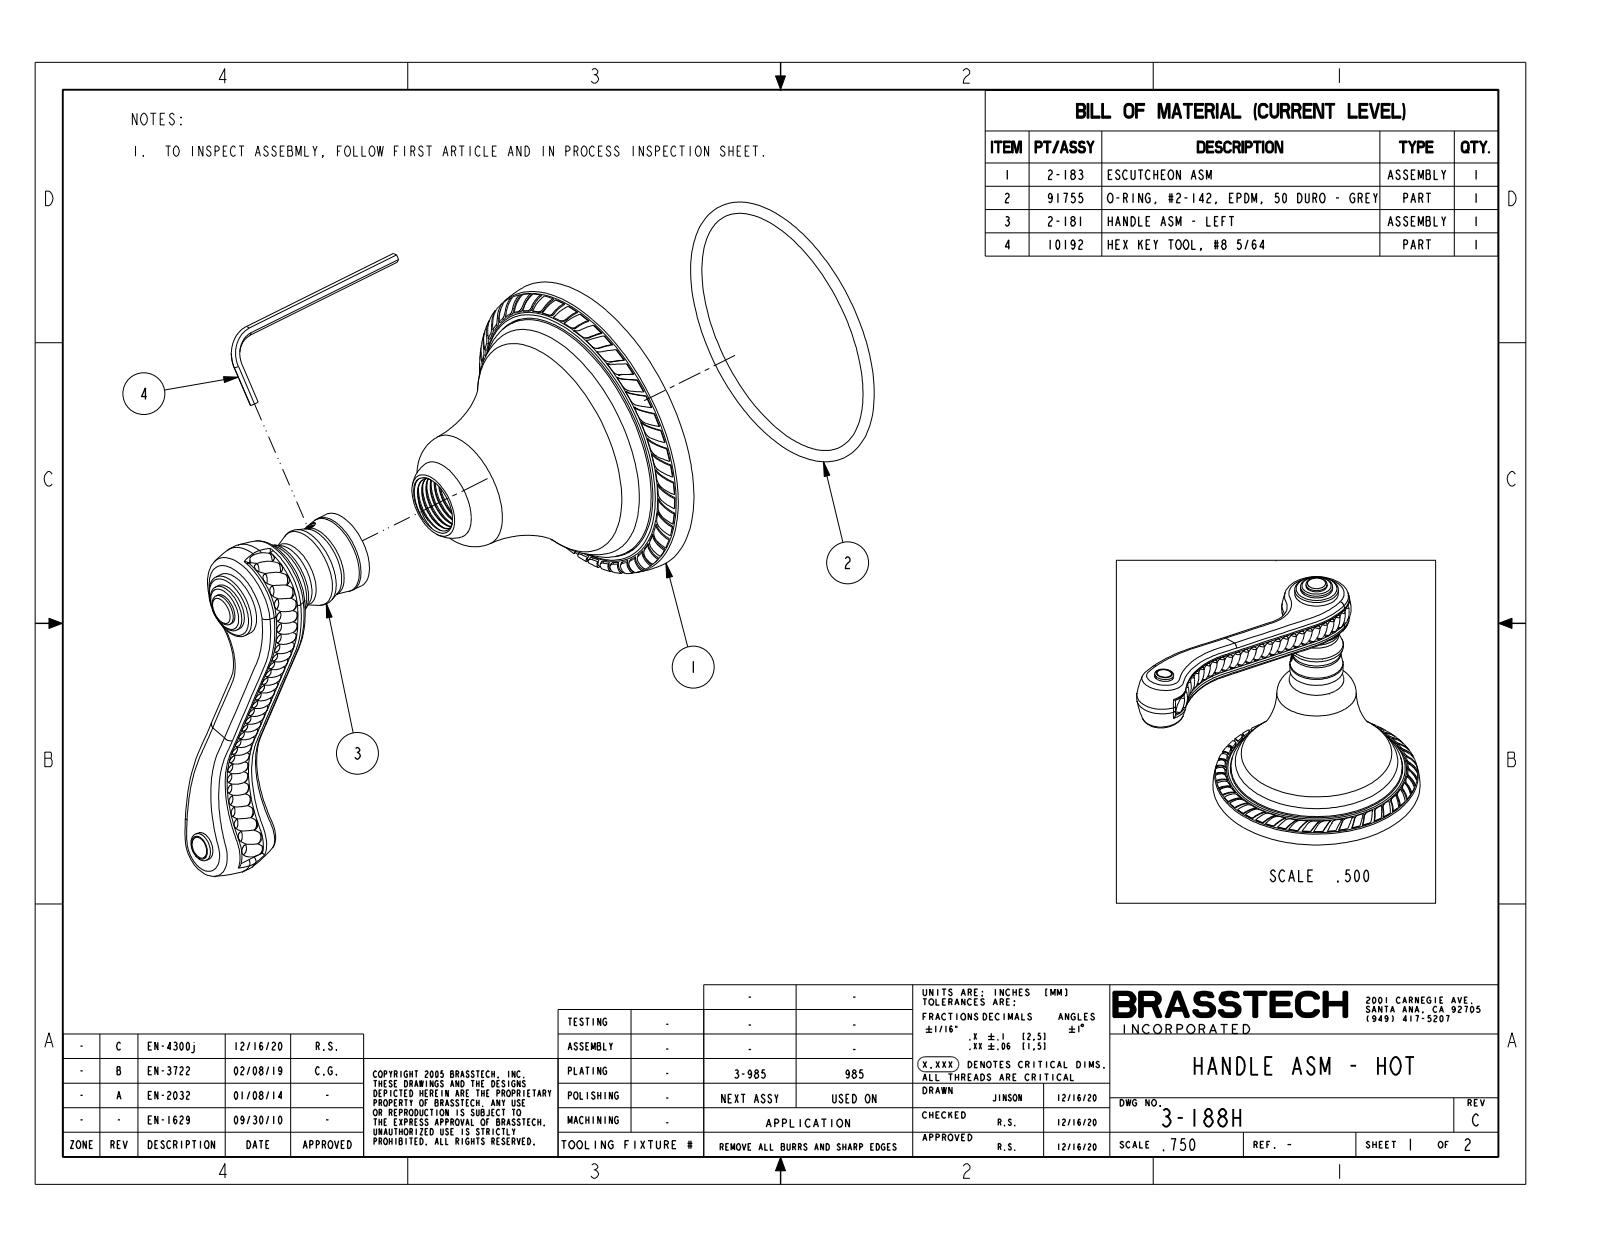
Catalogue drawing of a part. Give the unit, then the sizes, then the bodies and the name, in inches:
Units: inches
Overall size (bounding box): 4.77 × 3.4 × 2.845
Round bosses / shafts (diameter × count): ⌀0.26 ×2, ⌀2.35 ×1, ⌀0.73 ×1, ⌀0.7 ×1, ⌀0.6 ×1, ⌀0.44 ×1, ⌀0.29 ×1
Partial cylindrical surfaces — rounded edges, fillets, slot ends (radius × count): R0.15 ×49, R0.09 ×25, R0.12 ×24, R11 ×2, R0.121 ×1, R0.137 ×1
Main face-to-face distances: 3.23, 1.94, 1.29, 2.74, 0.8, 0.49, 0.29, 1.65, 2.45, 2.94
Volume: 5.898 in³ · Surface area: 29.51 in²
Bodies: 2 solids, 553 faces (113 planar, 118 cylindrical, 322 other)
Part name (STEP PRODUCT): 3-188H
STEP written by: CREO PARAMETRIC BY PTC INC, 2023134 (CONFIG_CONTROL_DESIGN)
